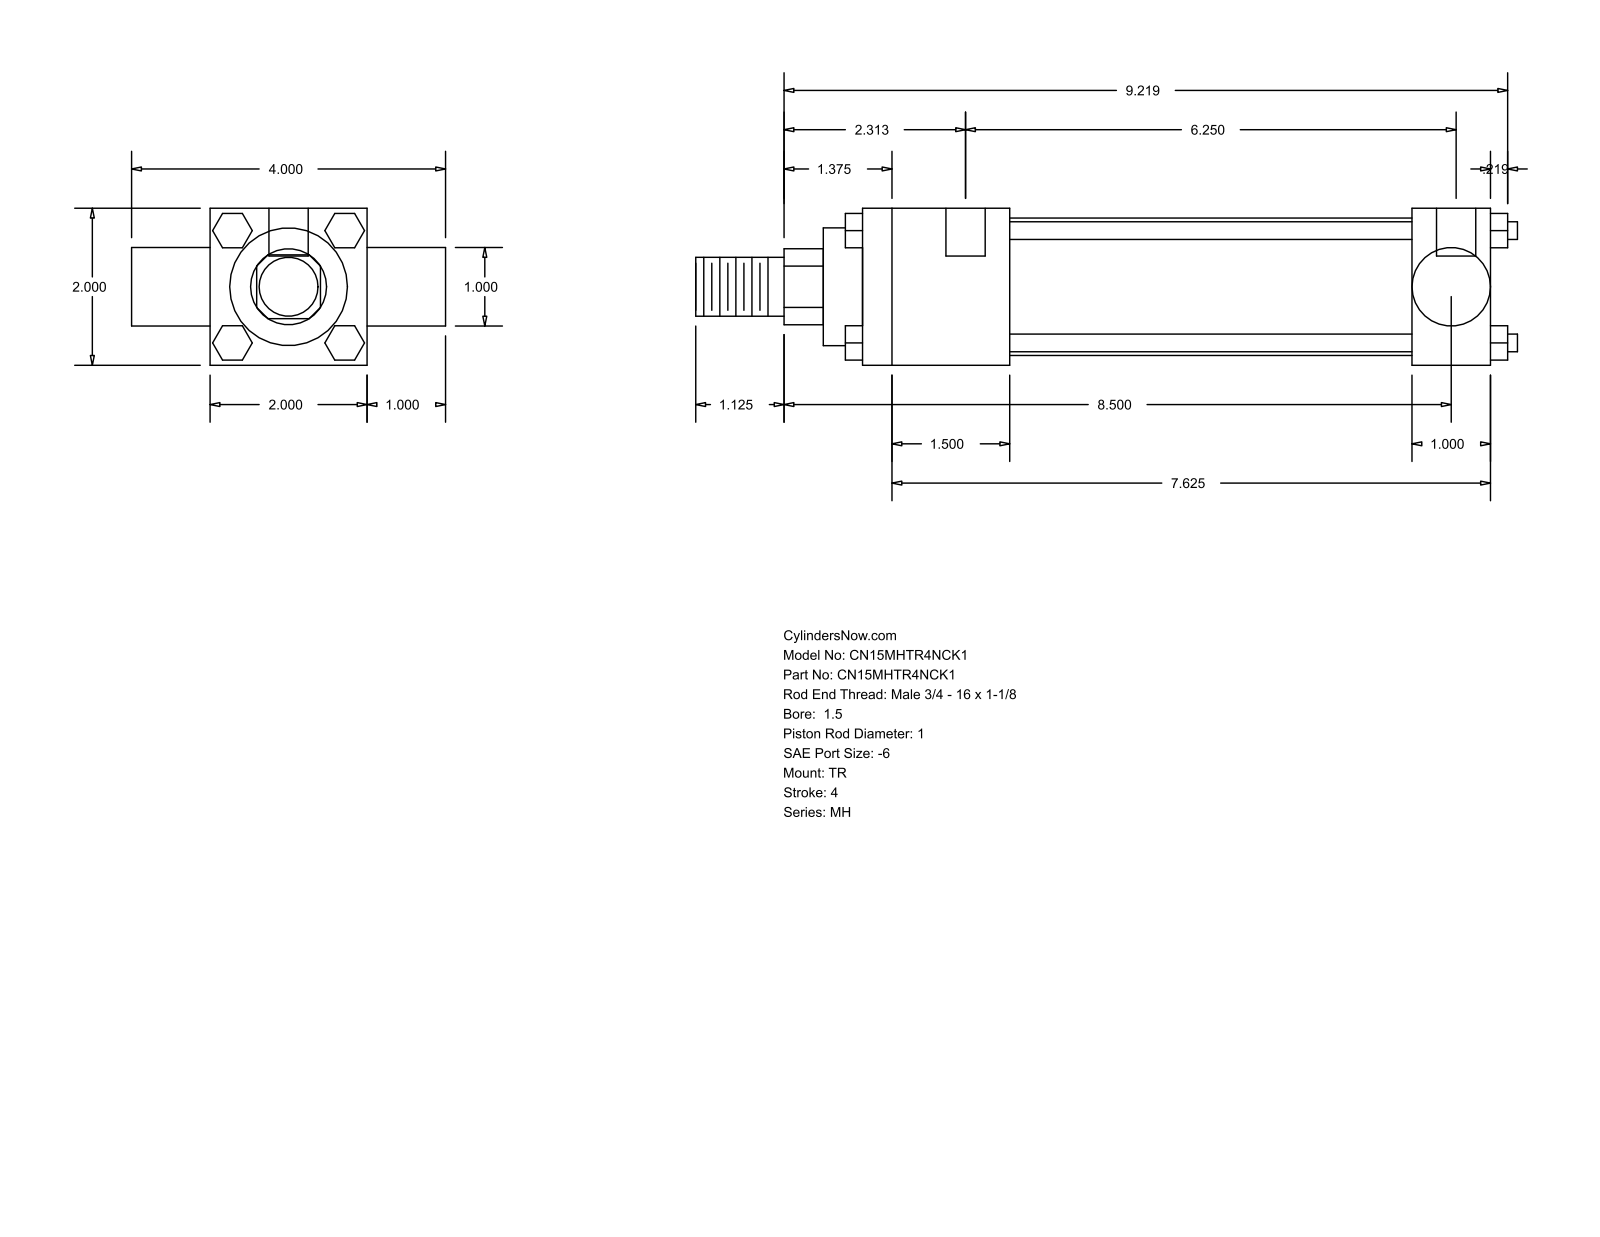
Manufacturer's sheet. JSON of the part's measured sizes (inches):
{"part_name": "MH_TR__0150_1", "step_written_by": "GSSL Pune (CONFIG_CONTROL_DESIGN)", "units": "inches", "bodies": {"solids": 0, "faces": 120, "planar": 92, "cylindrical": 28, "other": 0}, "overall_size": [10.469, 4, 2], "round_holes": [[0.219, 3], [0.5, 2]], "round_bosses_or_shafts": [[0.225, 4], [1.75, 1], [1.5, 1], [1, 1], [0.998, 1], [0.75, 1]], "partial_cylinders_radius": [[0.484, 1]], "face_to_face_distances": [2, 1, 8, 3, 1.875, 6.125, 7, 5.125, 4, 0.5], "hole_center_spacings": [0.125, 6.25, 6.375]}
